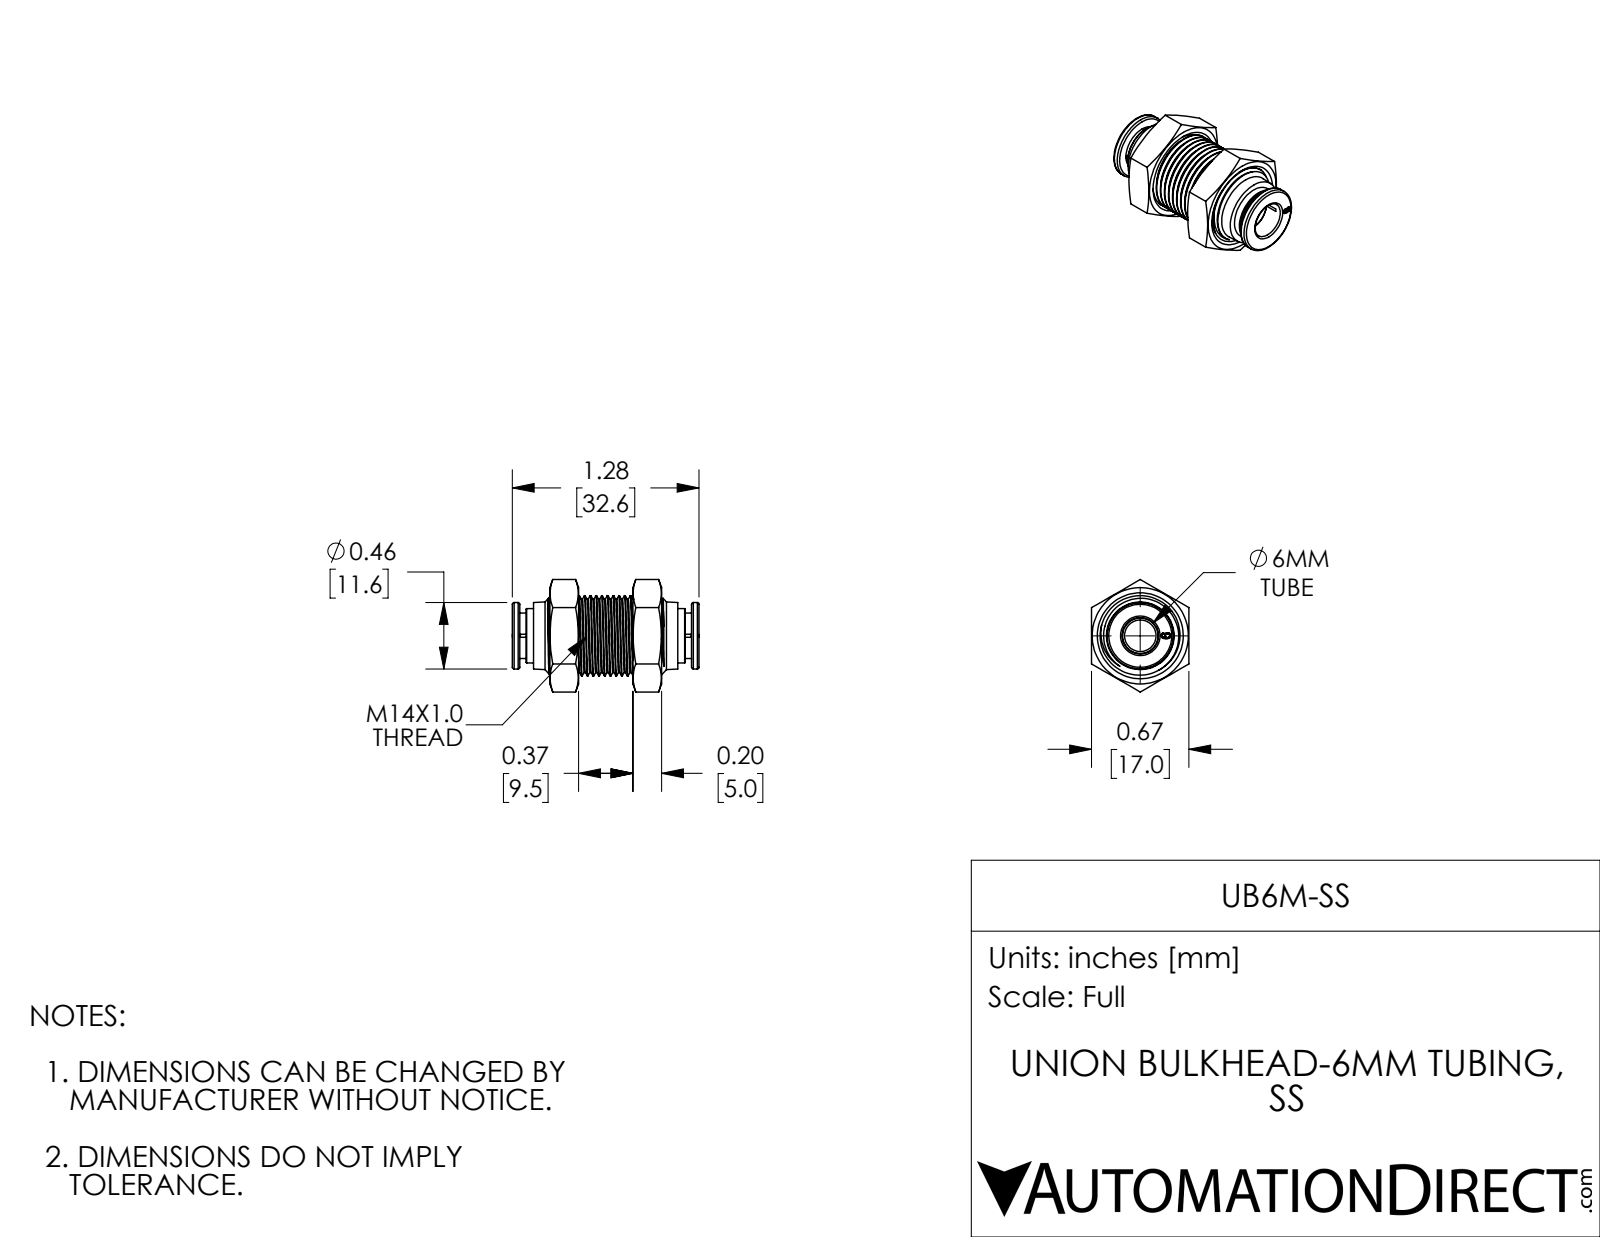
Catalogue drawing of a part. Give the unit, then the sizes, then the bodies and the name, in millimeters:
Units: millimetres
Overall size (bounding box): 32.6 × 19.6 × 17
Round holes (diameter × count): ⌀5.5 ×1, ⌀6.2 ×1, ⌀6.3 ×1, ⌀8.1 ×1, ⌀13 ×1
Round bosses / shafts (diameter × count): ⌀14 ×1, ⌀12.8 ×1, ⌀11.6 ×1, ⌀9.5 ×1, ⌀8 ×1
Main face-to-face distances: 17, 1.3, 5.3, 10.3, 14.5, 2.4, 28.9, 31.3, 6.6, 11.6
Volume: 3 950 mm³ · Surface area: 3 729 mm²
Bodies: 1 solid, 238 faces (46 planar, 109 cylindrical, 83 other)
Part name (STEP PRODUCT): UB6M-SS
STEP written by: SolidWorks 2017 (AUTOMOTIVE_DESIGN)
